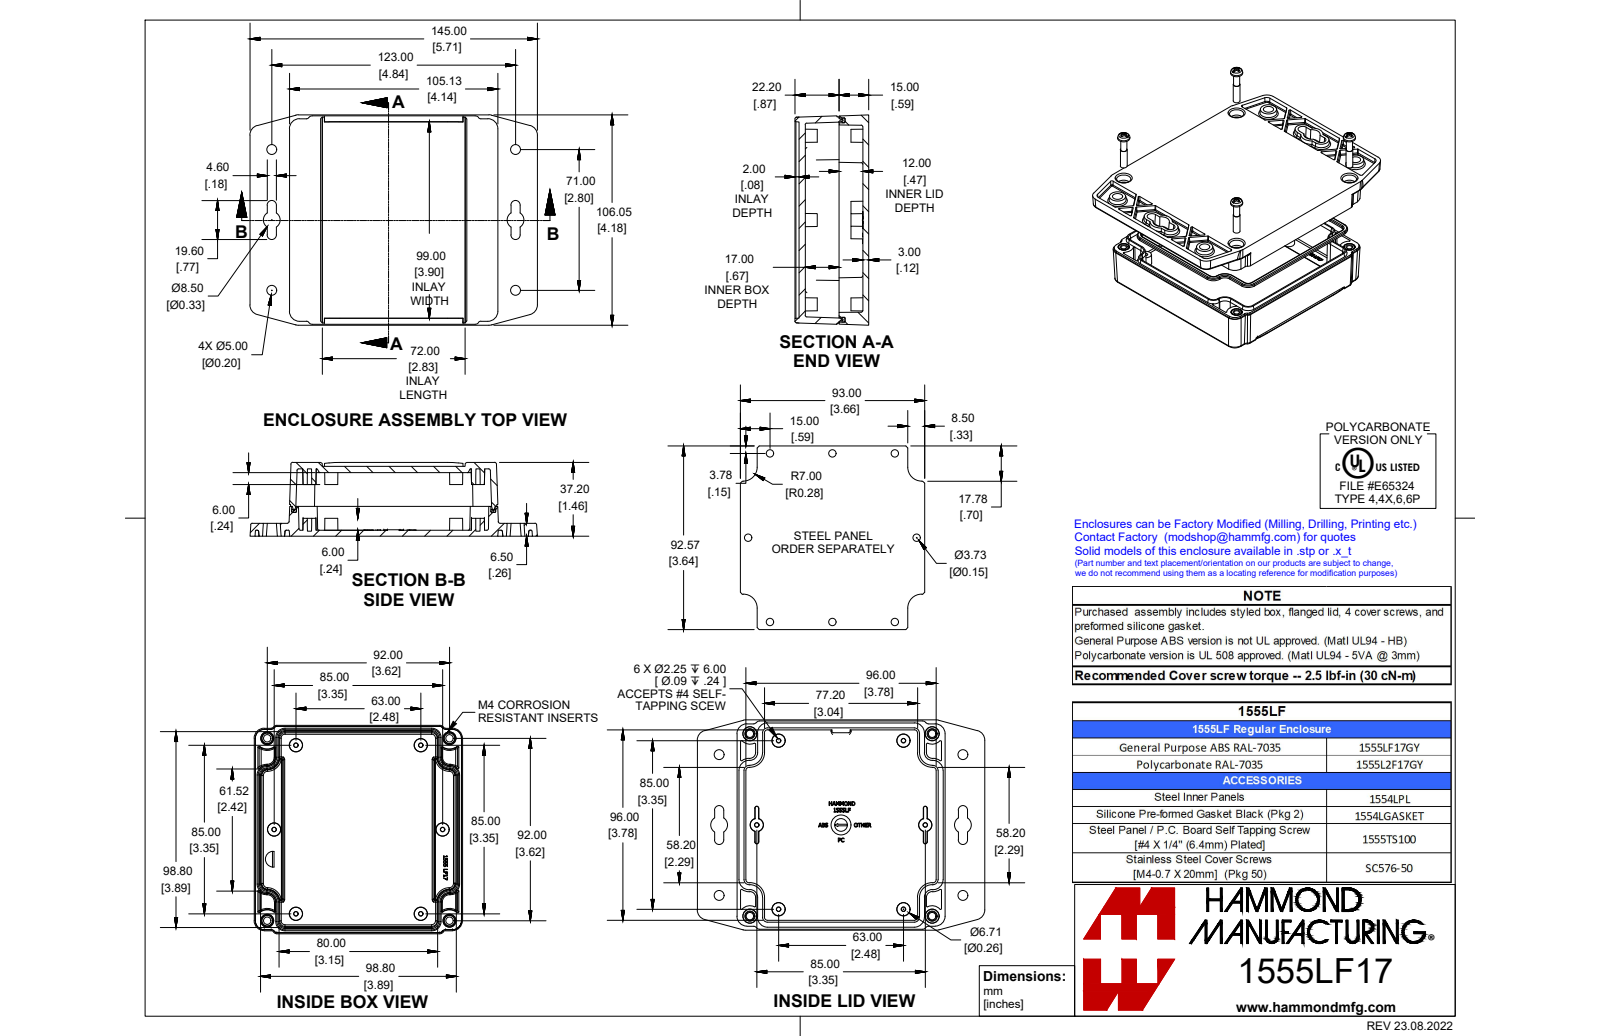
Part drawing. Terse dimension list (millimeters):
name: 1555LF17GY
written by: SolidWorks 2021 (AUTOMOTIVE_DESIGN)
unit: mm
bodies: 7 solids, 1303 faces (429 planar, 322 cylindrical, 552 other)
size: 145 × 106 × 37.2
volume: 142 700 mm³; area: 96 970 mm²
holes: 4× ⌀3.3, 4× ⌀4
bosses: 4× ⌀7, 4× ⌀3.9, 4× ⌀3.5
rounds: 114× R0.5, 48× R0.8, 16× R0.3, 8× R1, 8× R2.6, 8× R5, 8× R5.1, 4× R3
face distances: 3.2, 3, 32.2, 35.2, 29, 32, 3.1, 3.5, 6.5, 2
hole spacings: 92, 130.1
